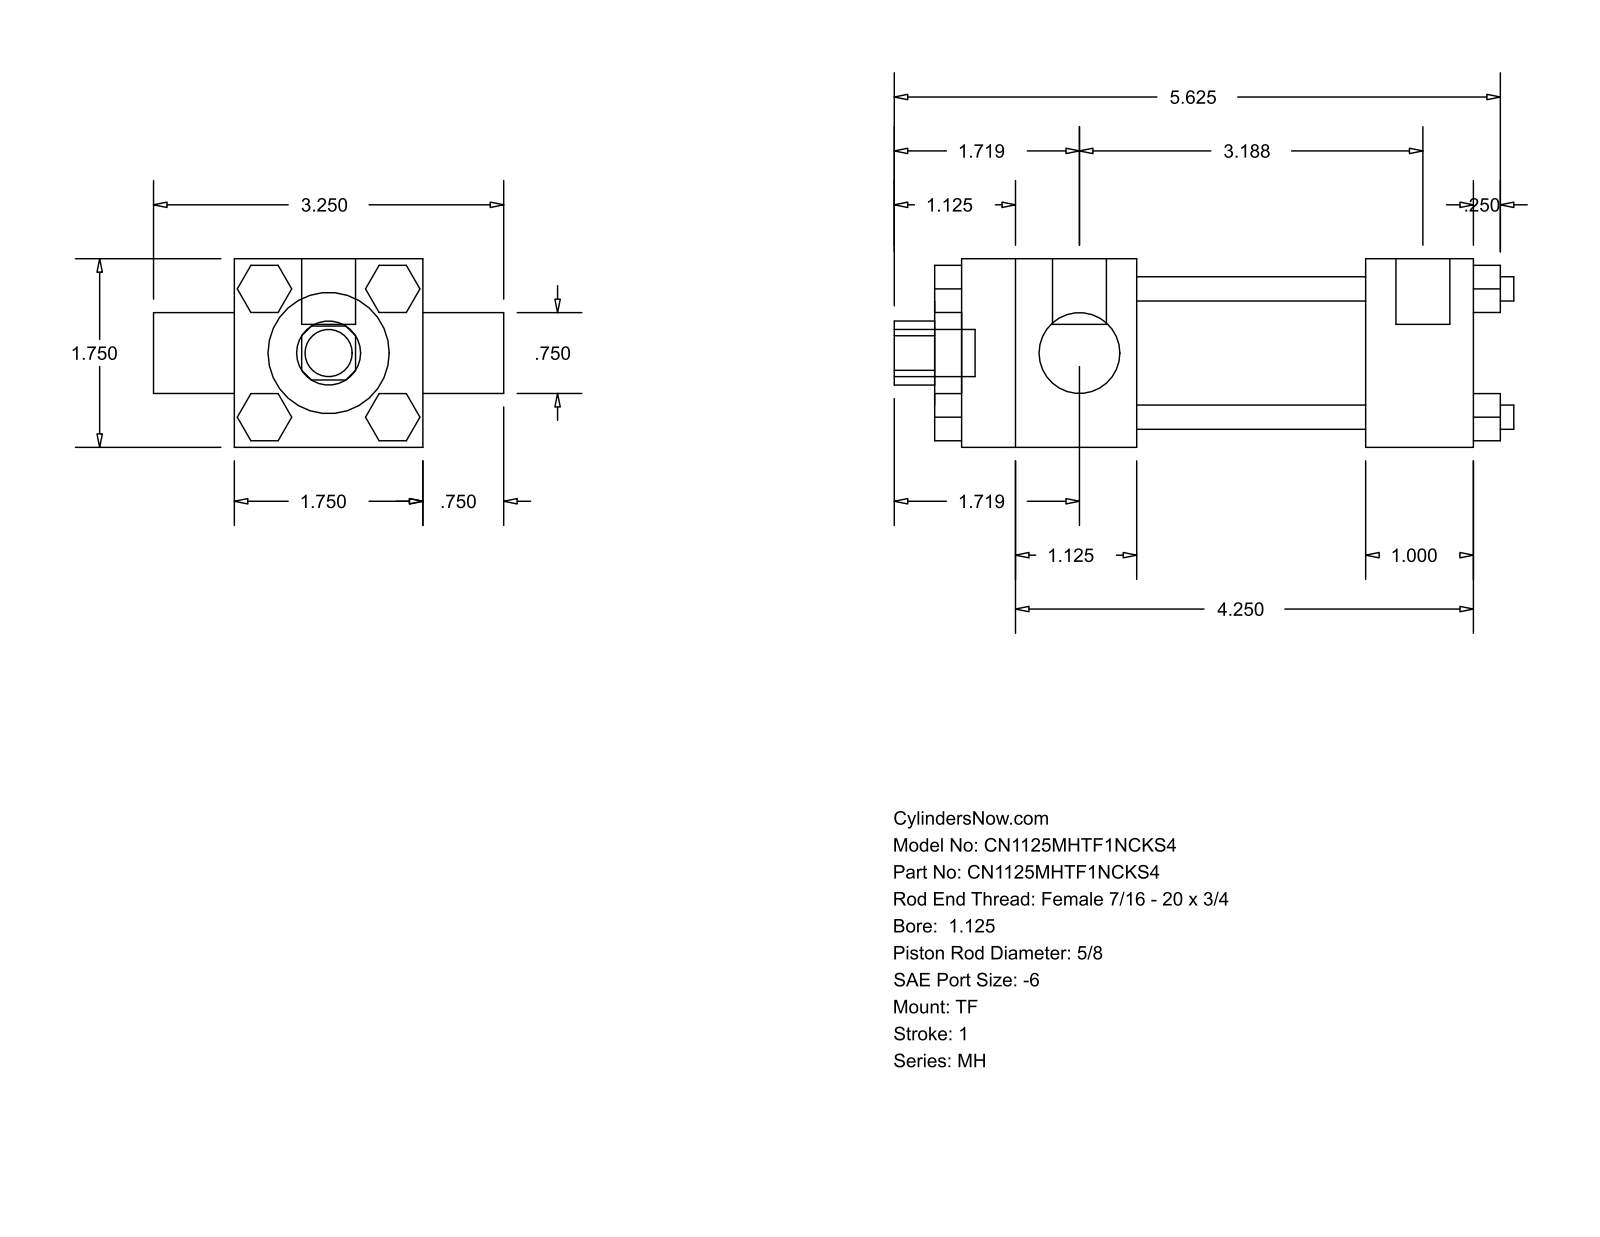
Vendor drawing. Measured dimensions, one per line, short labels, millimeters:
name: MH_TF__0112_0.625
written by: GSSL Pune (CONFIG_CONTROL_DESIGN)
unit: mm
bodies: 0 solids, 120 faces (92 planar, 28 cylindrical, 0 other)
size: 146.05 × 82.55 × 44.45
holes: 1× ⌀15.88, 1× ⌀19.05, 1× ⌀28.57, 1× ⌀34.92
bosses: 4× ⌀5.71, 3× ⌀5.56, 2× ⌀12.7, 1× ⌀11.11
rounds: 1× R7.54
face distances: 44.46, 127, 6.35, 11.11, 53.97, 79.38, 25.41, 41.27, 95.24, 120.65
